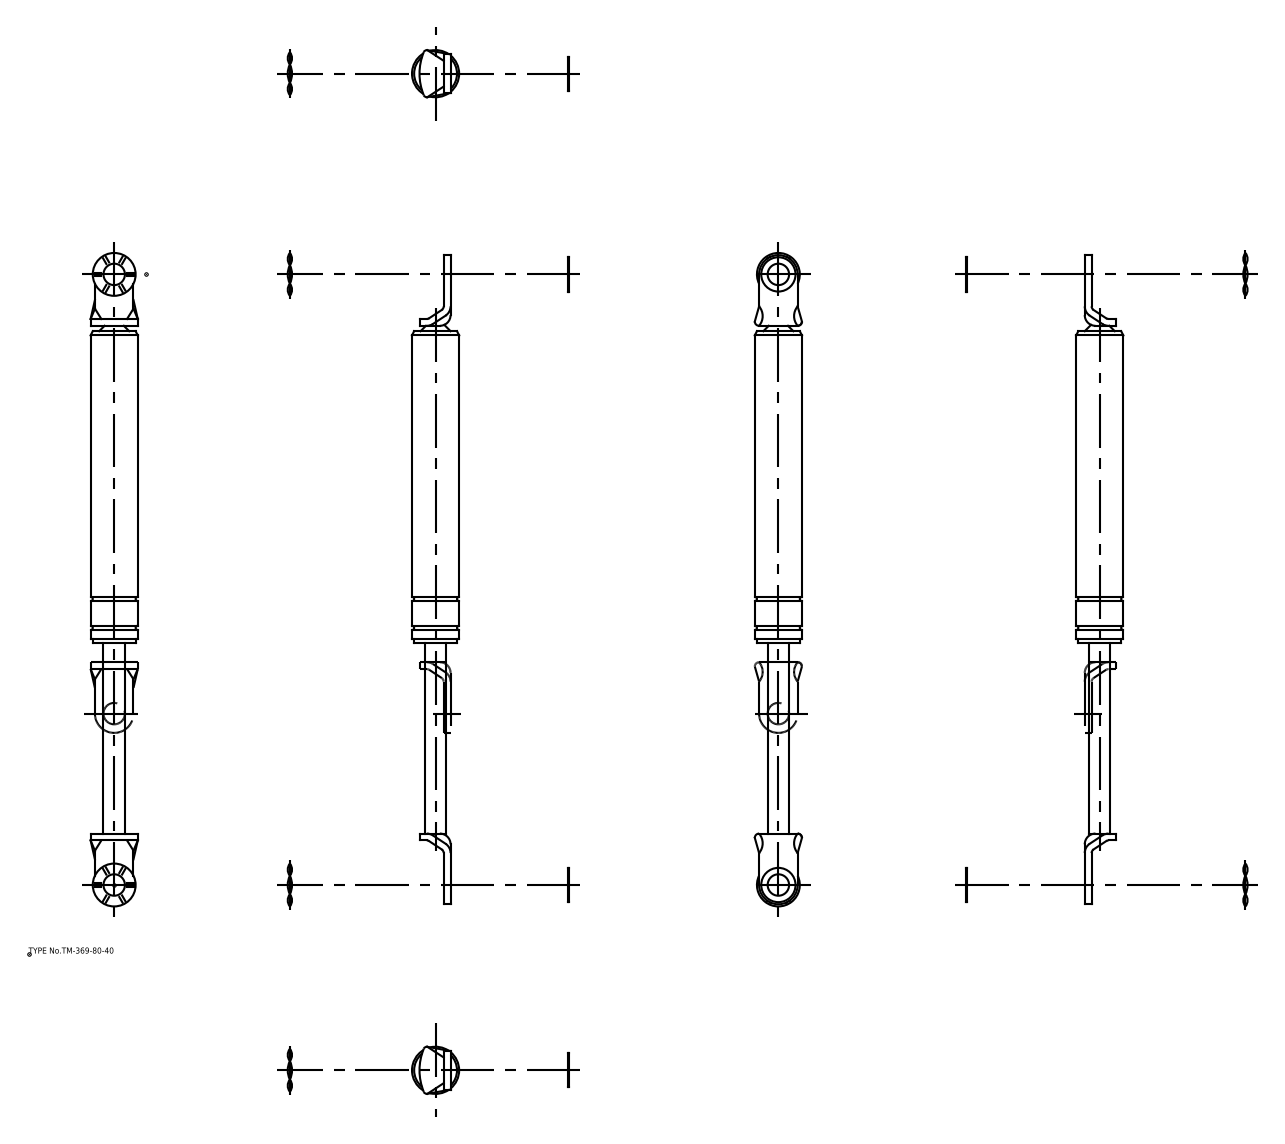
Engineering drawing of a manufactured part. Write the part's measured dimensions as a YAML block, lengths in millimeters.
part_name: "ウェーブワッシャー; ワッシャー; 本体; 本体_div"
step_written_by: "spGate 16.7.1 (AUTOMOTIVE_DESIGN)"
units: millimeters
bodies: {solids: 6, faces: 95, planar: 43, cylindrical: 44, other: 8}
overall_size: [305, 22.5, 22.5]
volume: 67988
surface_area: 19308
round_holes:
  - {diameter: 10, count: 2}
round_bosses_or_shafts:
  - {diameter: 20, count: 3}
  - {diameter: 16, count: 2}
  - {diameter: 22.5, count: 1}
  - {diameter: 22, count: 1}
  - {diameter: 10, count: 1}
partial_cylinders:
  - {radius: 4.4, count: 2}
  - {radius: 5, count: 2}
  - {radius: 9, count: 2}
  - {radius: 26.32, count: 1}
face_to_face_distances: [3.2, 2, 5.2, 5.7, 240.2, 3.7, 0.5, 151.2, 92.2, 243.4]
hole_center_spacings: [285]
